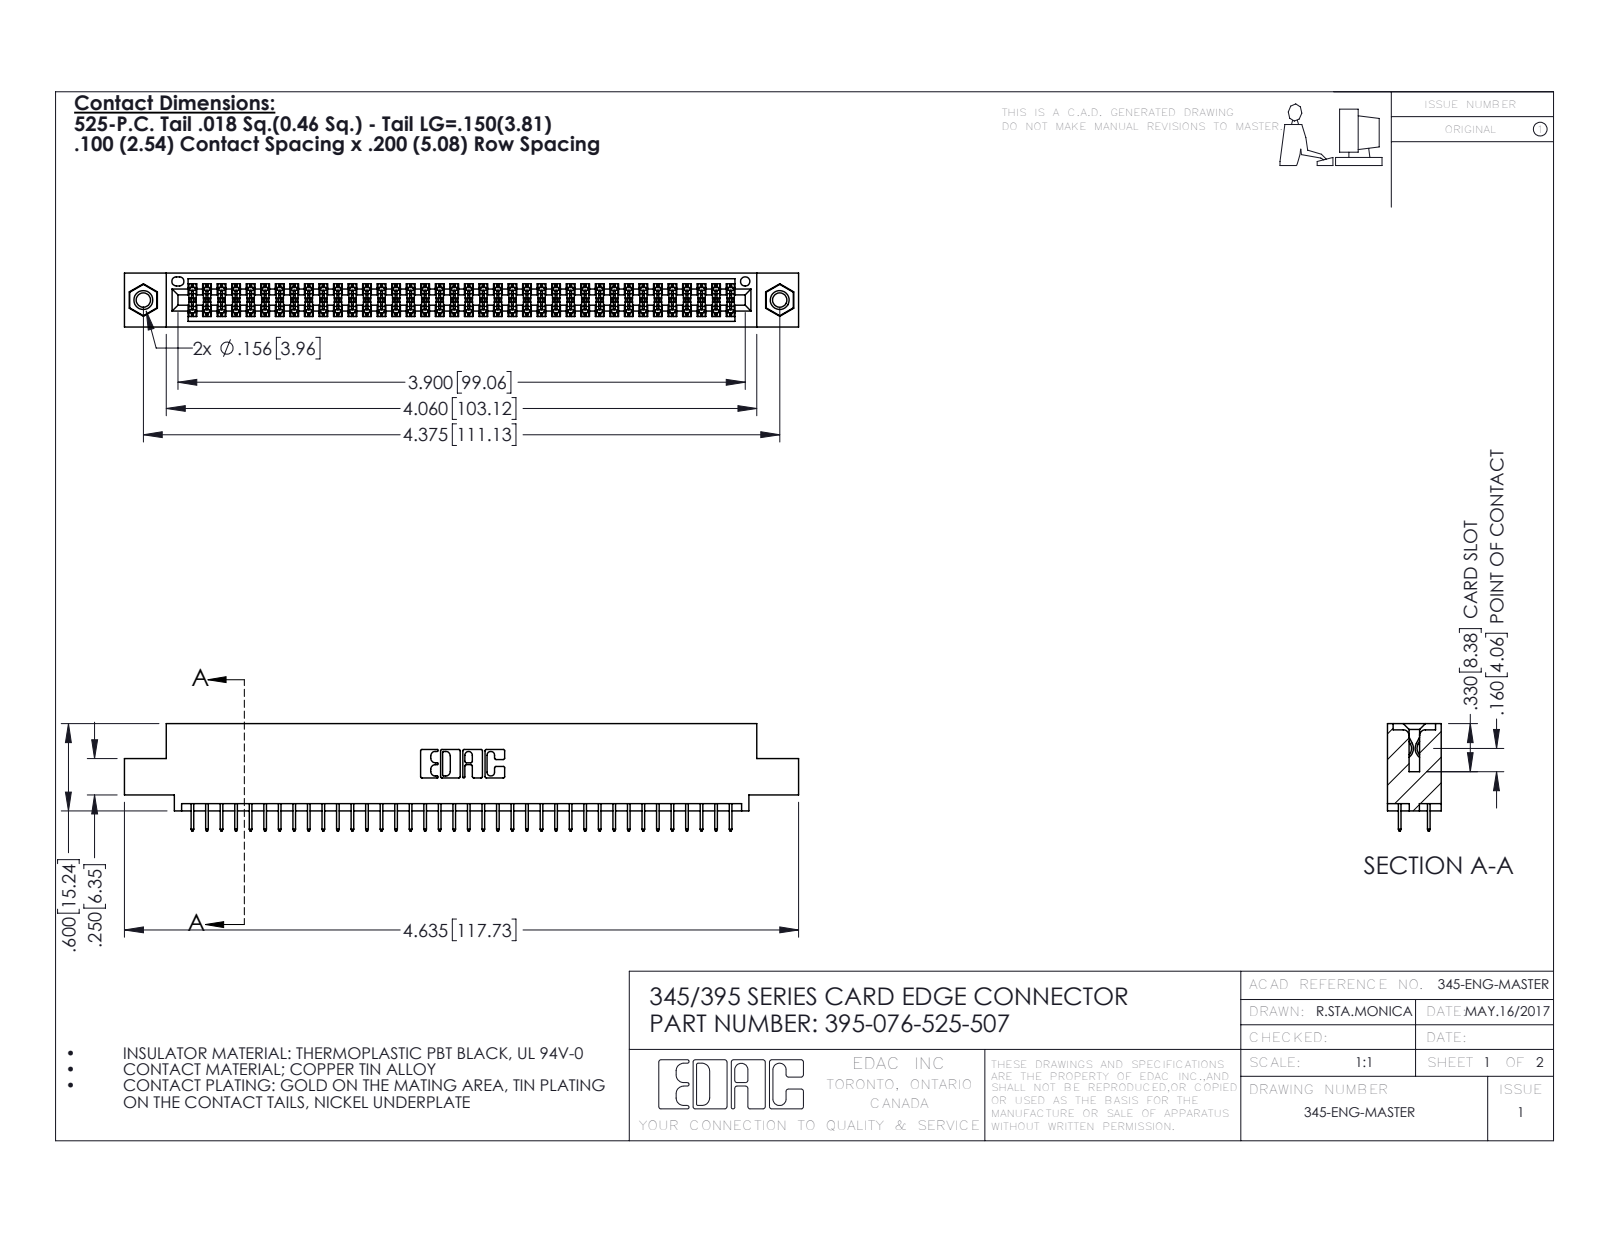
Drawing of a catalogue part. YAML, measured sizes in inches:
part_name: "345-292-001_345-293-125; 345 Part_0.110 Offset - 0.156 Dia-TI; 345-250-001_345-250-005-103; 395-076-525-507"
step_written_by: "SolidWorks 2020 (CONFIG_CONTROL_DESIGN)"
units: inches
bodies: {solids: 79, faces: 4294, planar: 3080, cylindrical: 1198, other: 16}
overall_size: [4.635, 0.737, 0.37]
volume: 0.683
surface_area: 25.11
round_holes:
  - {diameter: 0.098, count: 2}
  - {diameter: 0.125, count: 2}
  - {diameter: 0.156, count: 2}
  - {diameter: 0.064, count: 1}
round_bosses_or_shafts:
  - {diameter: 0.155, count: 2}
partial_cylinders:
  - {radius: 0.006, count: 114}
  - {radius: 0.01, count: 22}
  - {radius: 0.007, count: 6}
  - {radius: 0.031, count: 6}
  - {radius: 0.026, count: 3}
  - {radius: 0.014, count: 2}
  - {radius: 0.019, count: 2}
  - {radius: 0.022, count: 2}
face_to_face_distances: [0.072, 0.298, 0.2, 0.37, 0.098, 0.272, 0.025, 0.225, 0.072, 0.175]
hole_center_spacings: [0.27, 4.139, 4.375]
